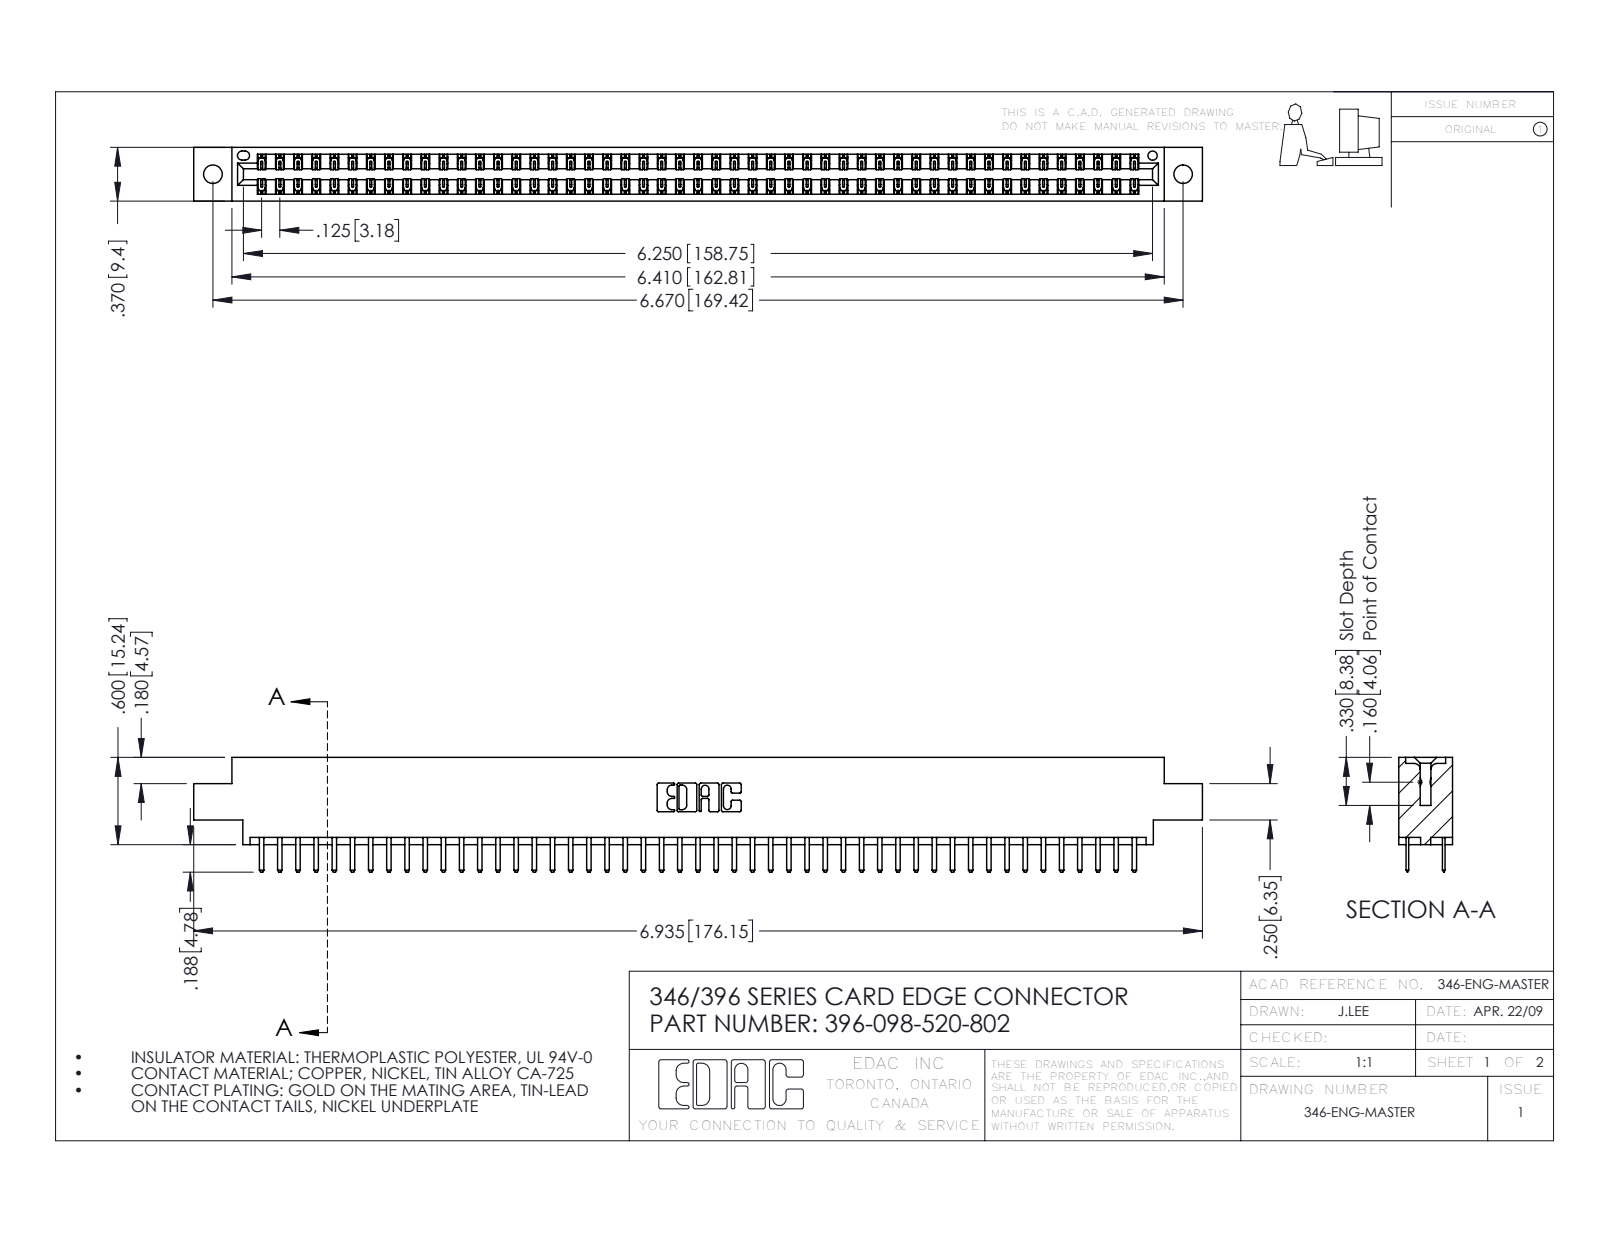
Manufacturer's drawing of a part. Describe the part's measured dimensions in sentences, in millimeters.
The part is named "346 Part_0.170 Offset - 0.128 Dia; 396-098-520-802; 345-292-001_345-293-120". Its 3-D file was written by "SolidWorks 2016 (CONFIG_CONTROL_DESIGN)". It is 99 solids with 5614 faces: 3706 planar, 1908 cylindrical and 0 other. Overall it measures 176.1 by 20 by 9.4 millimeters. Its volume is 16 990 cubic millimeters and its surface area 23 280 square millimeters. Round holes: 2 of diameter 3.3, 1 of diameter 1.6. Partial cylindrical surfaces (rounded edges, fillets, slot ends): 147 of radius 0.2, 102 of radius 0.3, 22 of radius 0.3, 6 of radius 0.2, 6 of radius 0.8, 3 of radius 0.7, 2 of radius 0.4, 2 of radius 0.6. The main face-to-face distances are 1.2, 8.2, 6.4, 9.4, 7, 1.8, 7.6, 0.6, 3.8, 5.6. The hole center spacings are 6.2, 164.1, 169.4.
